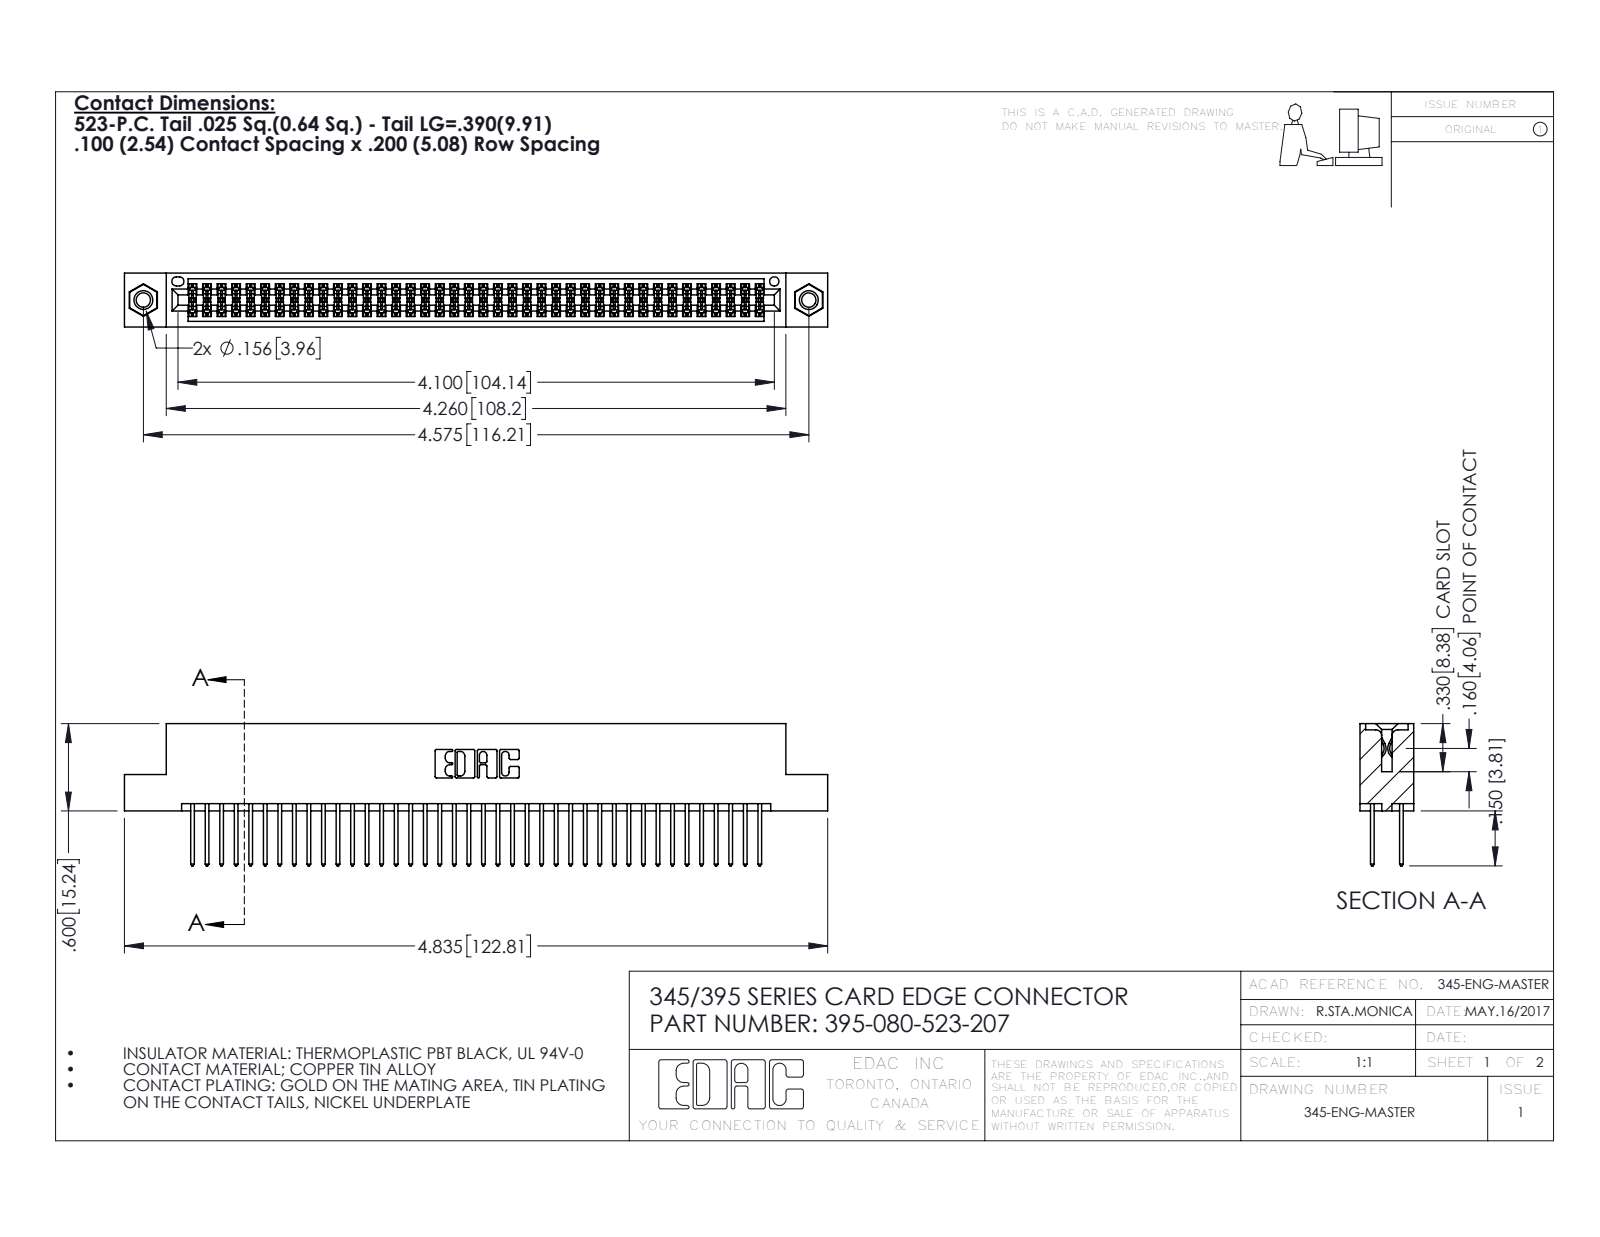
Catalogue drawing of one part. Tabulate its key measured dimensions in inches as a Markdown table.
| quantity | value |
| --- | --- |
| part name | 395-080-523-207; 345-292-001_345-293-123; 345-250-001_345-250-005-103; 345 Part_Flush Mounting Lugs - 0.156 Dia-TI |
| STEP written by | SolidWorks 2016 (CONFIG_CONTROL_DESIGN) |
| units | inches |
| bodies | 83 solids, 4186 faces (2752 planar, 1418 cylindrical, 16 other) |
| overall size | 4.835 × 0.977 × 0.37 |
| volume | 0.736 in³ |
| surface area | 28.76 in² |
| round holes (diameter × count) | 0.098 × 2, 0.125 × 2, 0.156 × 2, 0.064 × 1 |
| round bosses / shafts (diameter × count) | 0.155 × 2 |
| partial cylindrical surfaces (radius × count) | 0.006 × 120, 0.01 × 80, 0.01 × 22, 0.007 × 6, 0.031 × 6, 0.026 × 3, 0.014 × 2, 0.019 × 2 |
| main face-to-face distances | 0.072, 0.298, 0.2, 0.098, 0.272, 0.025, 0.37, 0.225, 0.175, 0.149 |
| hole center spacings | 0.27, 4.339, 4.575 |
